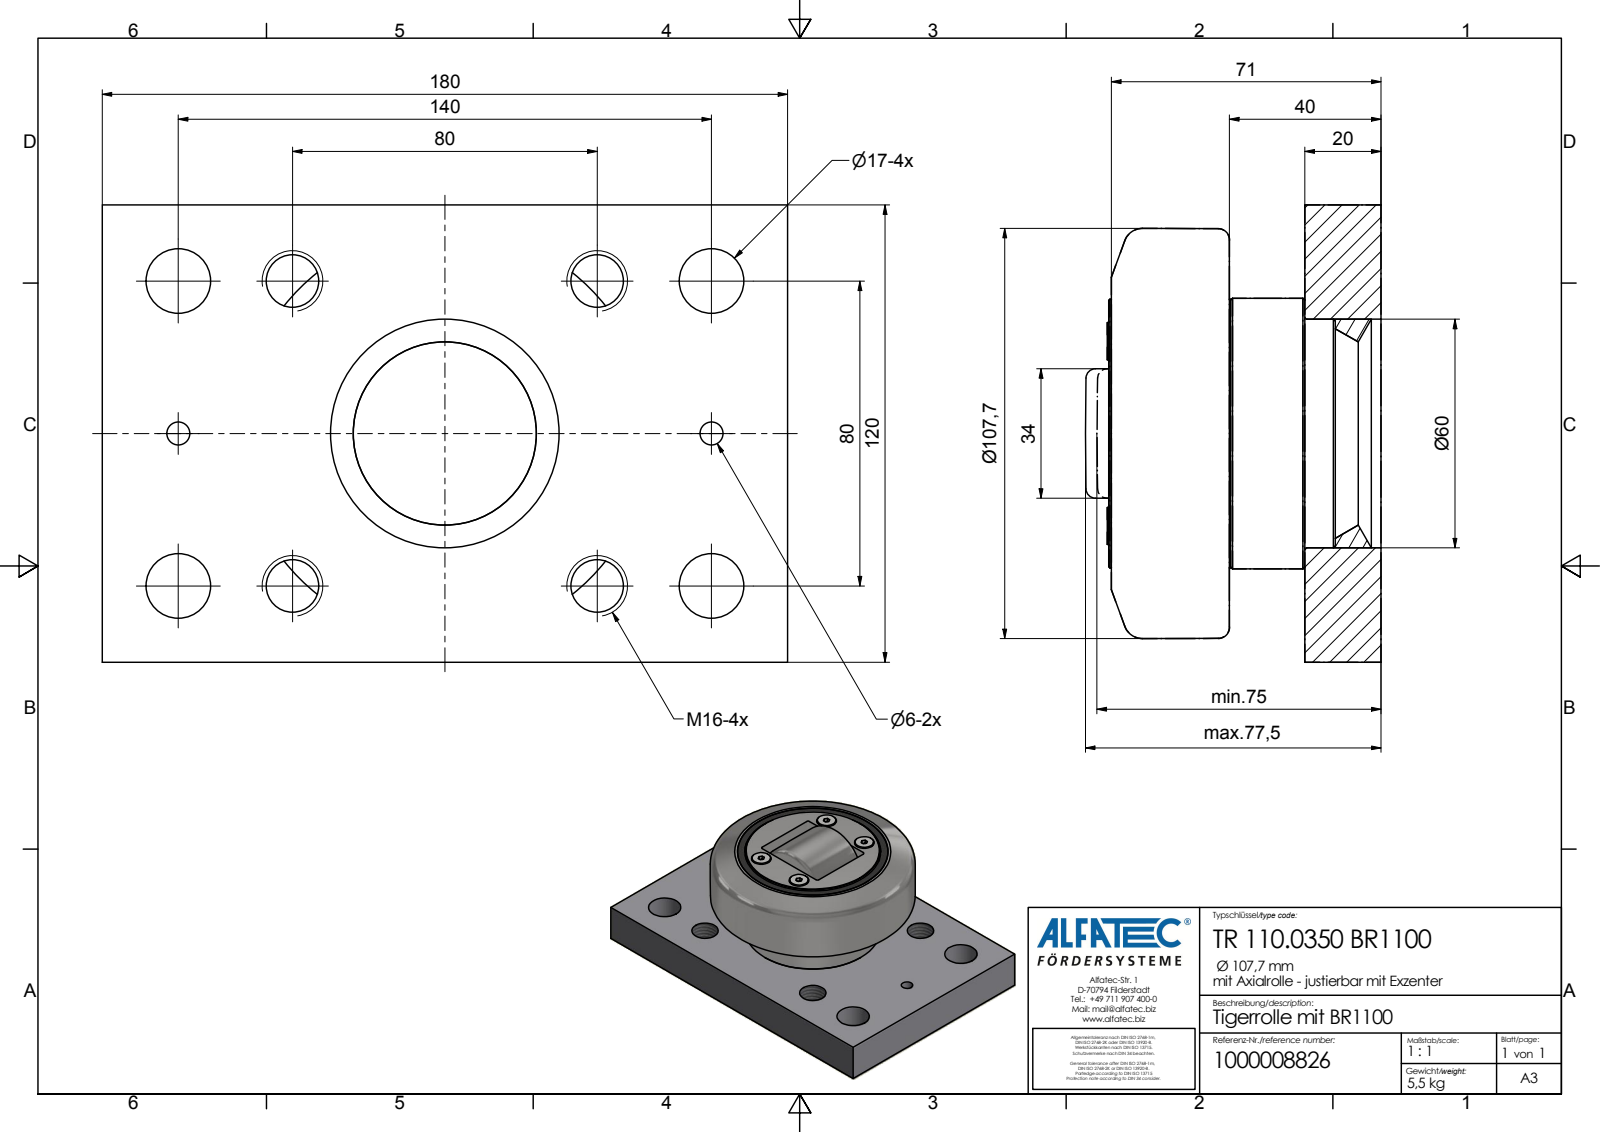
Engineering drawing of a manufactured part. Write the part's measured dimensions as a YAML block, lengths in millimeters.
part_name: "TR 110.0350 BR1100_Kontur"
step_written_by: "Autodesk Inventor 2020 (AP242_MANAGED_MODEL_BASED_3D_ENGINEERING_MIM_LF)"
units: millimeters
bodies: {solids: 1, faces: 75, planar: 44, cylindrical: 17, other: 14}
overall_size: [180, 120, 77.59]
volume: 757314
surface_area: 84519
round_holes:
  - {diameter: 13.84, count: 4}
  - {diameter: 17, count: 4}
  - {diameter: 6, count: 2}
round_bosses_or_shafts:
  - {diameter: 9.75, count: 4}
  - {diameter: 71, count: 1}
  - {diameter: 70.5, count: 1}
face_to_face_distances: [20, 39.8, 19.8, 120, 51.5, 71.5, 31.7, 180, 70.8, 50.8]
hole_center_spacings: [80, 30, 40, 50, 85.44, 110, 117.05, 136.01]
